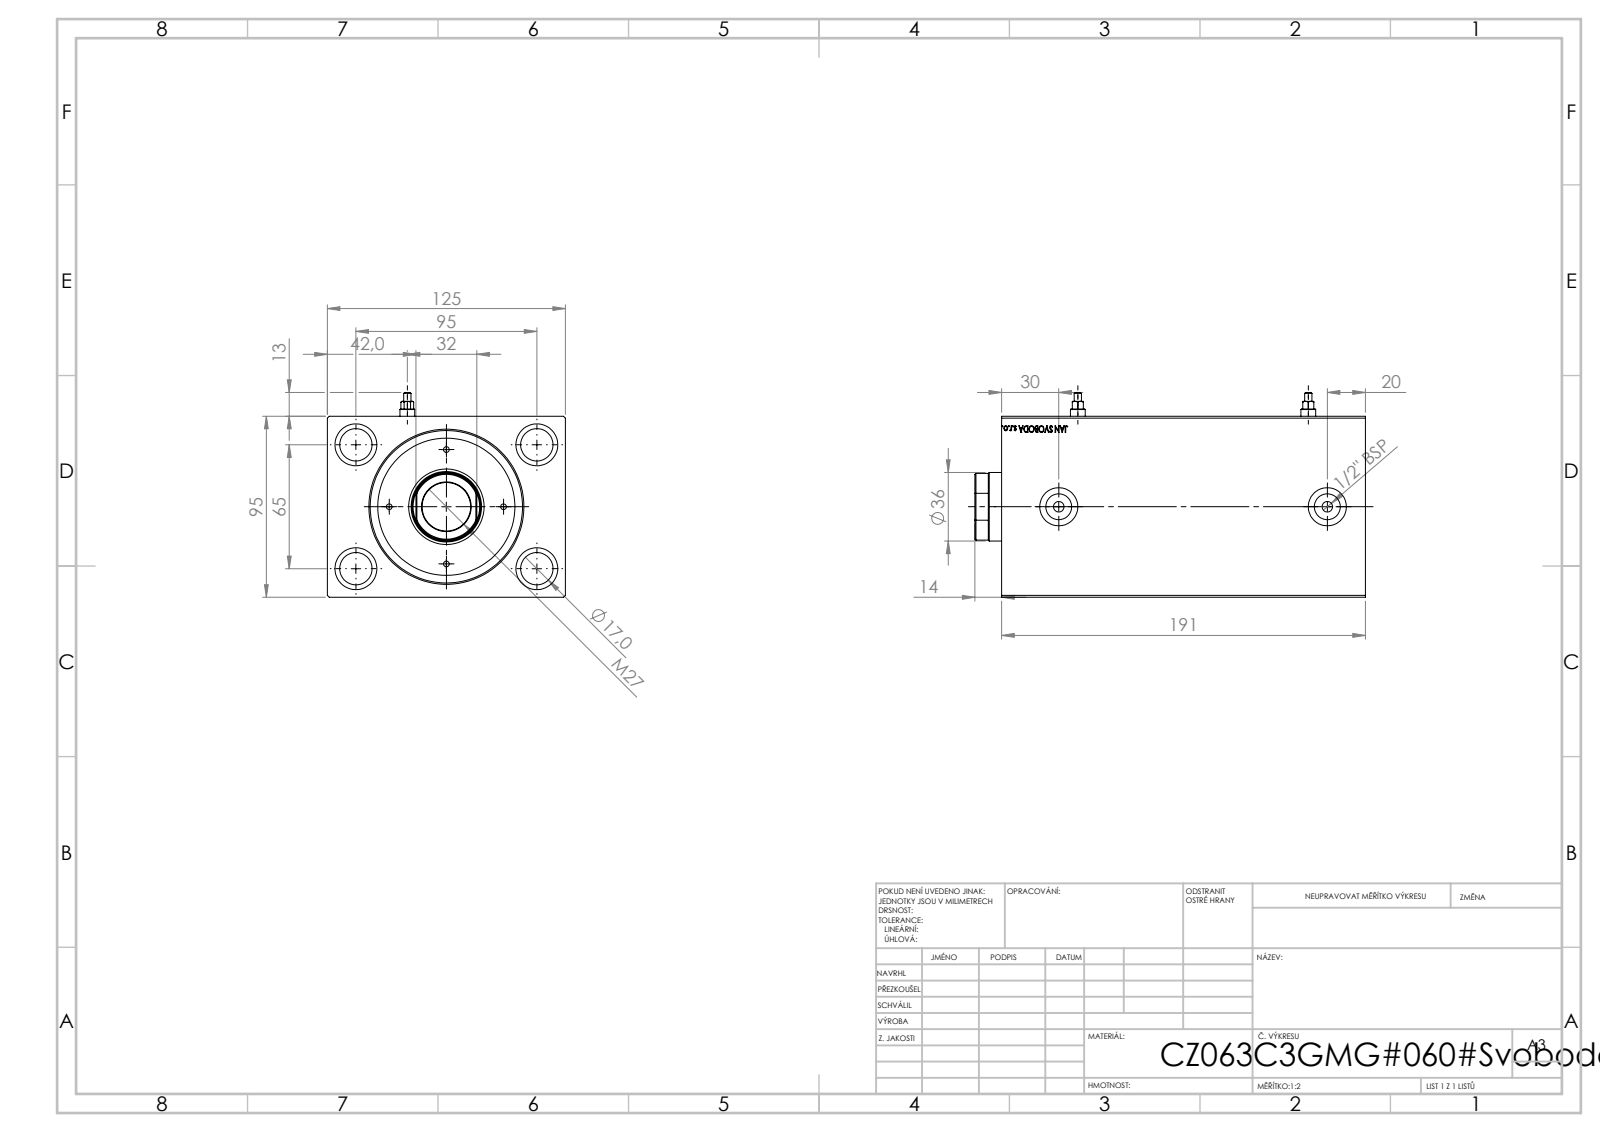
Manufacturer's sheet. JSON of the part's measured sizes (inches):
{"step_written_by": "SolidWorks 2019 (CONFIG_CONTROL_DESIGN)", "units": "inches", "bodies": {"solids": 1, "faces": 825, "planar": 397, "cylindrical": 46, "other": 382}, "overall_size": [7.52, 4.921, 3.74], "volume_in3": 92.76, "surface_area_in2": 284.6, "round_holes": [[0.669, 4], [0.866, 4], [0.217, 2], [0.315, 2], [0.535, 2], [0.787, 2], [1.417, 1], [2.48, 1], [3.15, 1]], "face_to_face_distances": [3.74, 4.921, 7.52, 6.701, 0.819, 0.551, 6.15, 6.969, 0.407, 7.113], "hole_center_spacings": [2.266, 2.559, 3.74, 4.532, 4.764, 5.551]}
